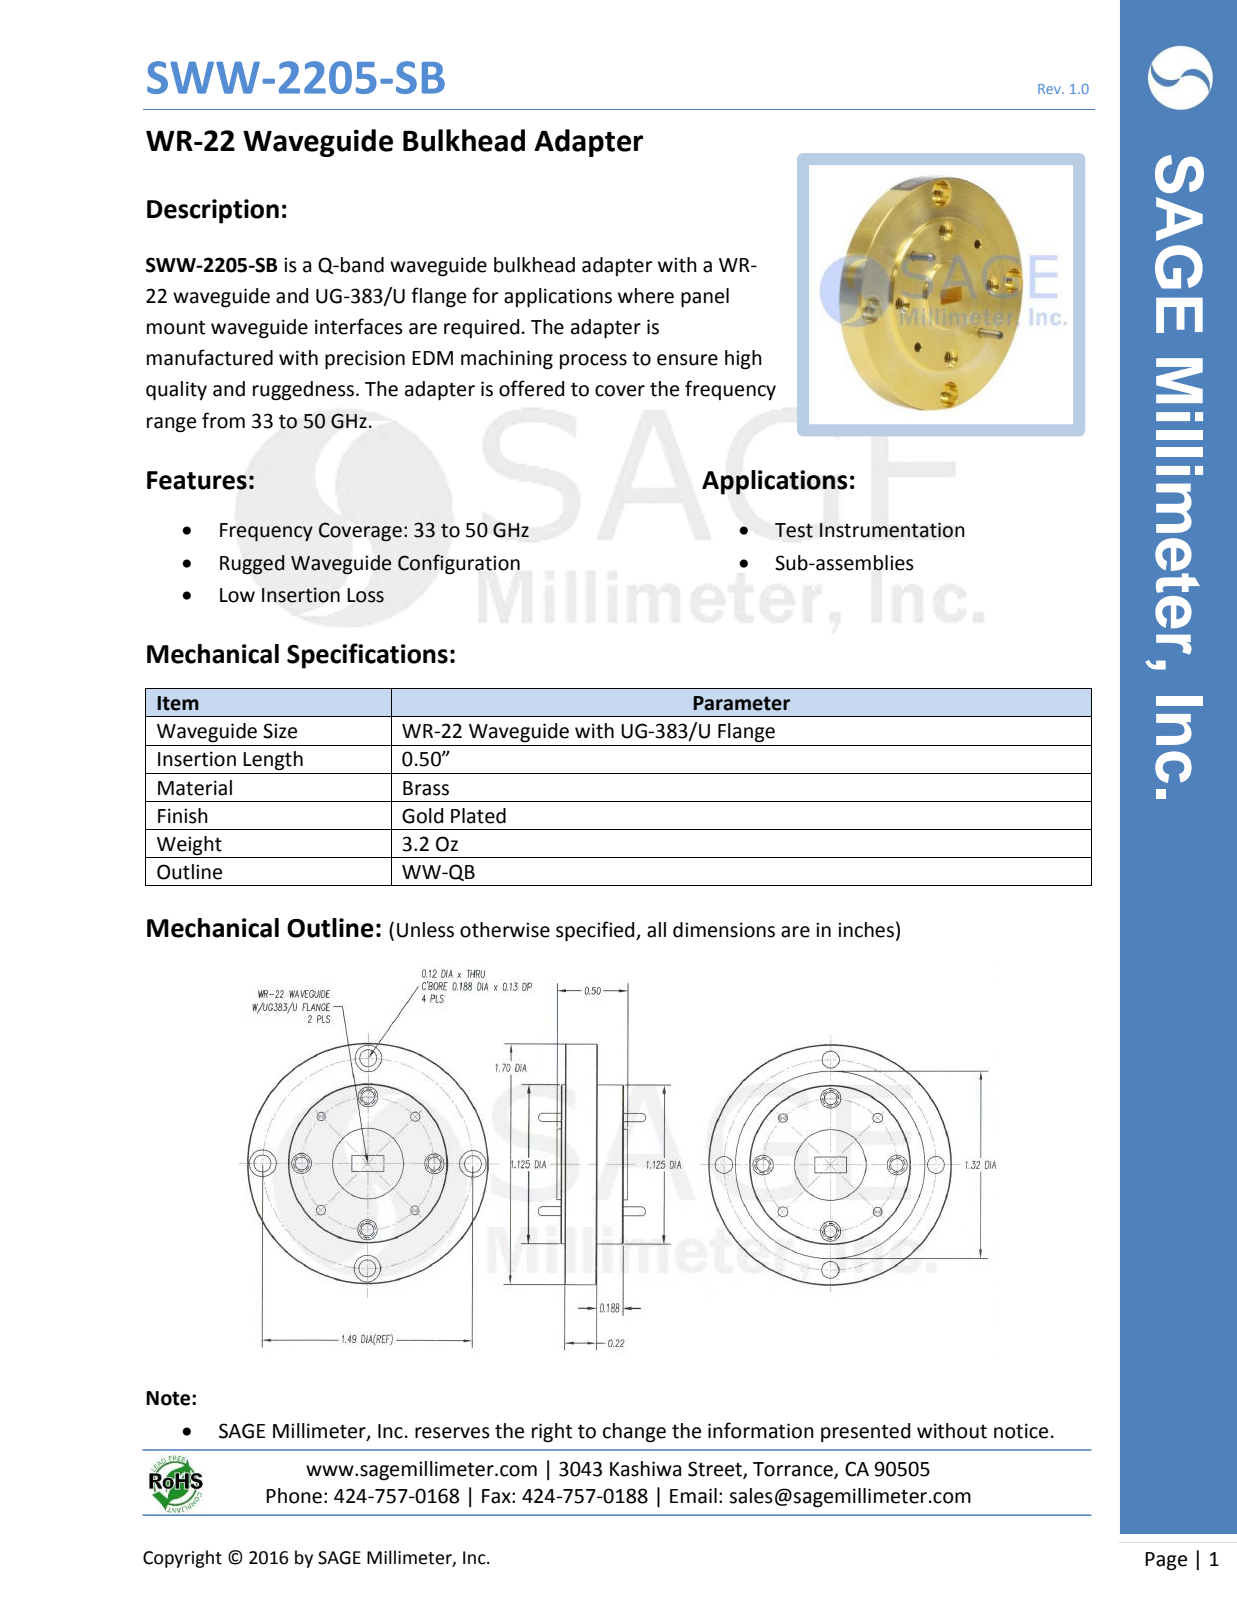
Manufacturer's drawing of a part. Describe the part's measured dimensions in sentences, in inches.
The part is named "WW-QB-A". Its 3-D file was written by "SolidWorks 2021 (AUTOMOTIVE_DESIGN)". It is 5 solids with 203 faces: 39 planar, 92 cylindrical and 72 other. Overall it measures 1.7 by 1.7 by 0.765 inches. Its volume is 0.691 cubic inches and its surface area 8.805 square inches. Round holes: 4 of diameter 0.061, 4 of diameter 0.067, 4 of diameter 0.089, 4 of diameter 0.12, 4 of diameter 0.14, 4 of diameter 0.187, 1 of diameter 1.055, 1 of diameter 1.325. Round bosses or shafts: 4 of diameter 0.063, 1 of diameter 1.7, 1 of diameter 1.125, 1 of diameter 0.5. The main face-to-face distances are 0.222, 0.04, 0.42, 0.262, 0.46, 0.198, 0.02, 0.48, 0.187, 0.147. The hole center spacings are 0.359, 0.469, 0.528, 0.663, 0.866, 0.878, 1.124, 0.274.
